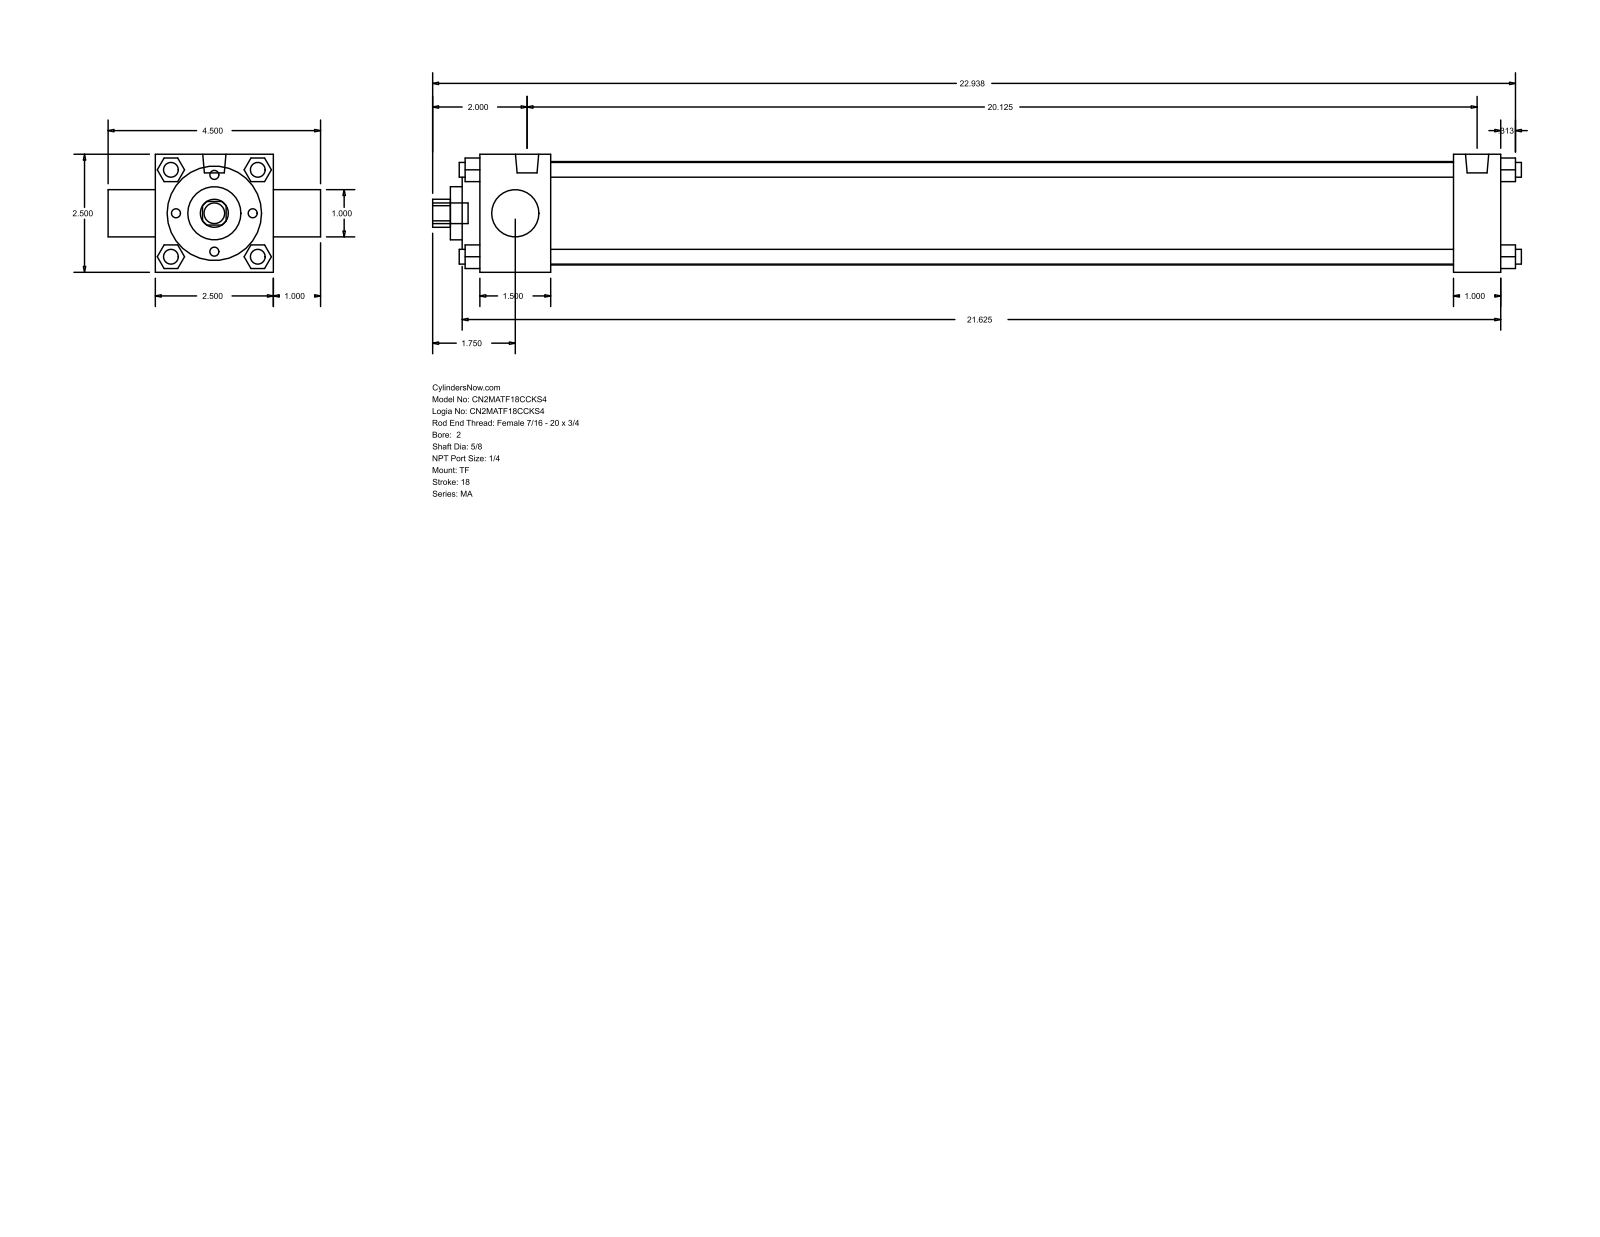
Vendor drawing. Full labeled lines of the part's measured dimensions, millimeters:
Part name (STEP PRODUCT): MA_TF__0200_0.625
STEP written by: GSSL Pune (CONFIG_CONTROL_DESIGN)
Units: millimetres
Bodies: 0 solids, 122 faces (93 planar, 29 cylindrical, 0 other)
Overall size (bounding box): 585.79 × 114.3 × 63.5
Round holes (diameter × count): ⌀15.88 ×1, ⌀25.4 ×1, ⌀28.57 ×1, ⌀50.8 ×1, ⌀55.63 ×1
Round bosses / shafts (diameter × count): ⌀7.94 ×7, ⌀12.49 ×2, ⌀11.11 ×1
Partial cylindrical surfaces — rounded edges, fillets, slot ends (radius × count): R7.54 ×1
Main face-to-face distances: 63.5, 25.4, 38.1, 12.7, 549.27, 9.52, 523.87, 485.77, 511.17, 47.62
